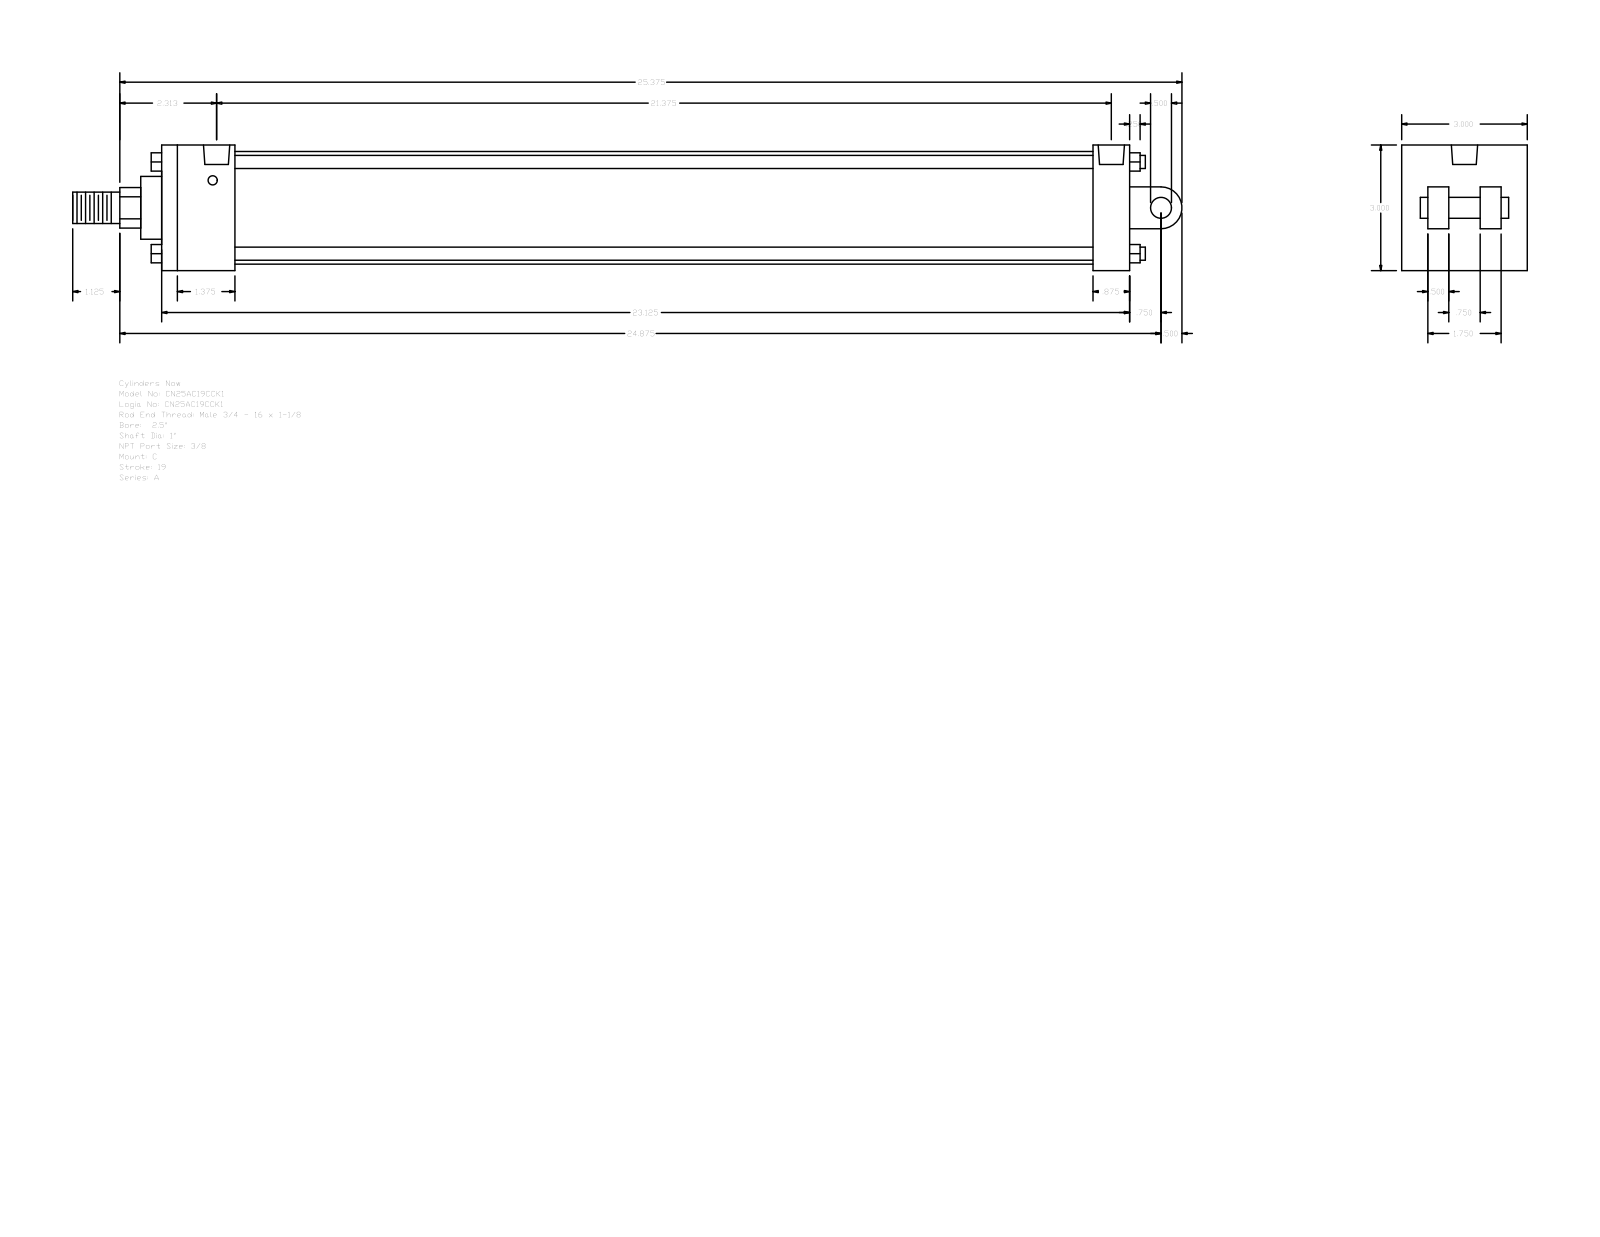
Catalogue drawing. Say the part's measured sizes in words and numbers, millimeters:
The part is named "A_C__0250_1". Its 3-D file was written by "GSSL Pune (CONFIG_CONTROL_DESIGN)". It is 0 solids with 135 faces: 102 planar, 33 cylindrical and 0 other. Overall it measures 673.1 by 76.2 by 76.2 millimeters. Round holes: 4 of diameter 5.56, 2 of diameter 15.93. Round bosses or shafts: 4 of diameter 7.94, 1 of diameter 68.33, 1 of diameter 38.1, 1 of diameter 25.4, 1 of diameter 19.05, 1 of diameter 12.7. Partial cylindrical surfaces (rounded edges, fillets, slot ends): 1 of radius 12.29, 1 of radius 12.7. The main face-to-face distances are 76.2, 587.37, 12.7, 44.45, 565.15, 520.7, 542.92, 22.22, 15.87, 25.4. The hole center spacings are 2.38, 545.3, 547.68, 542.92.
